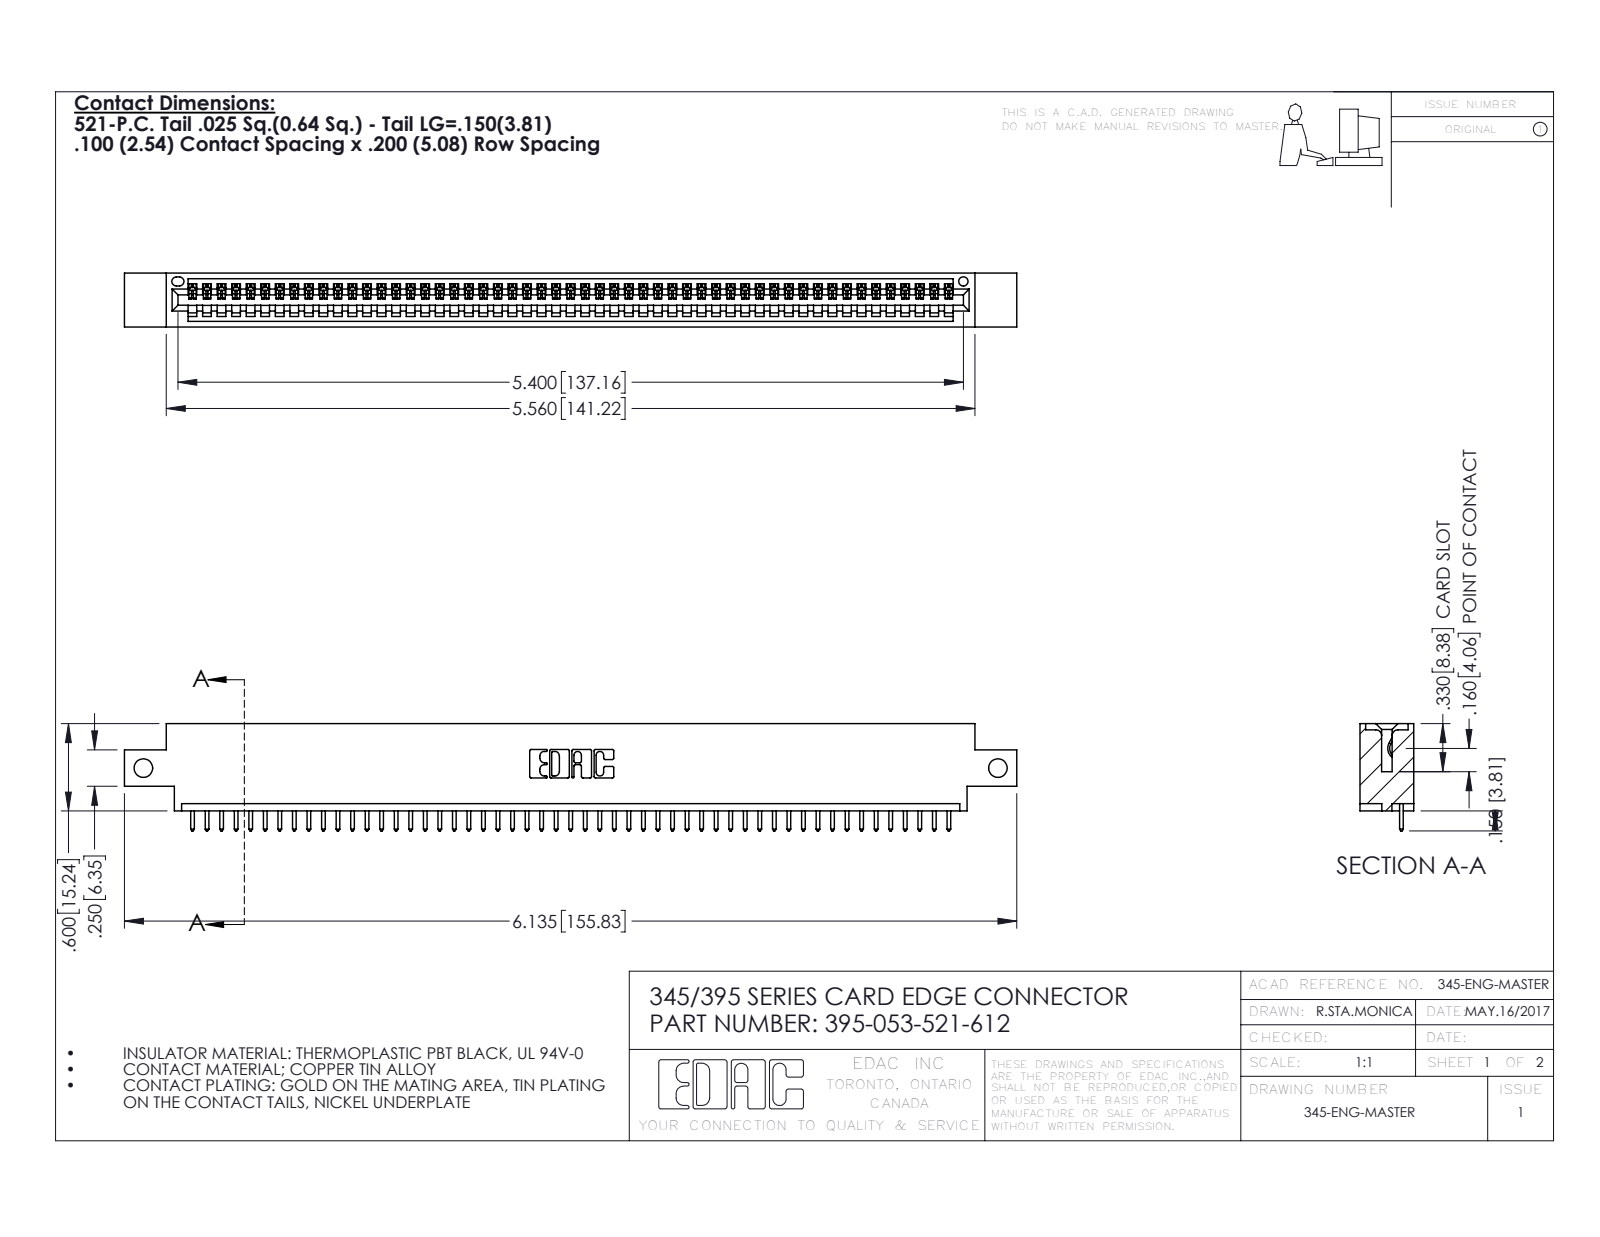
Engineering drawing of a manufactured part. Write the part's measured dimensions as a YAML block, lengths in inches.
part_name: "395-053-521-612; 345 Part_0.170 Offset - Side Mount; 345-292-001_345-293-121"
step_written_by: "SolidWorks 2016 (CONFIG_CONTROL_DESIGN)"
units: inches
bodies: {solids: 54, faces: 3204, planar: 2204, cylindrical: 1000, other: 0}
overall_size: [6.135, 0.737, 0.37]
volume: 0.887
surface_area: 29.24
round_holes:
  - {diameter: 0.128, count: 2}
  - {diameter: 0.064, count: 1}
partial_cylinders:
  - {radius: 0.006, count: 106}
  - {radius: 0.01, count: 106}
  - {radius: 0.01, count: 22}
  - {radius: 0.007, count: 6}
  - {radius: 0.031, count: 6}
  - {radius: 0.026, count: 3}
  - {radius: 0.031, count: 2}
  - {radius: 0.04, count: 2}
face_to_face_distances: [0.298, 0.072, 0.37, 0.2, 0.098, 0.272, 0.025, 0.225, 0.175, 0.149]
hole_center_spacings: [5.875]
